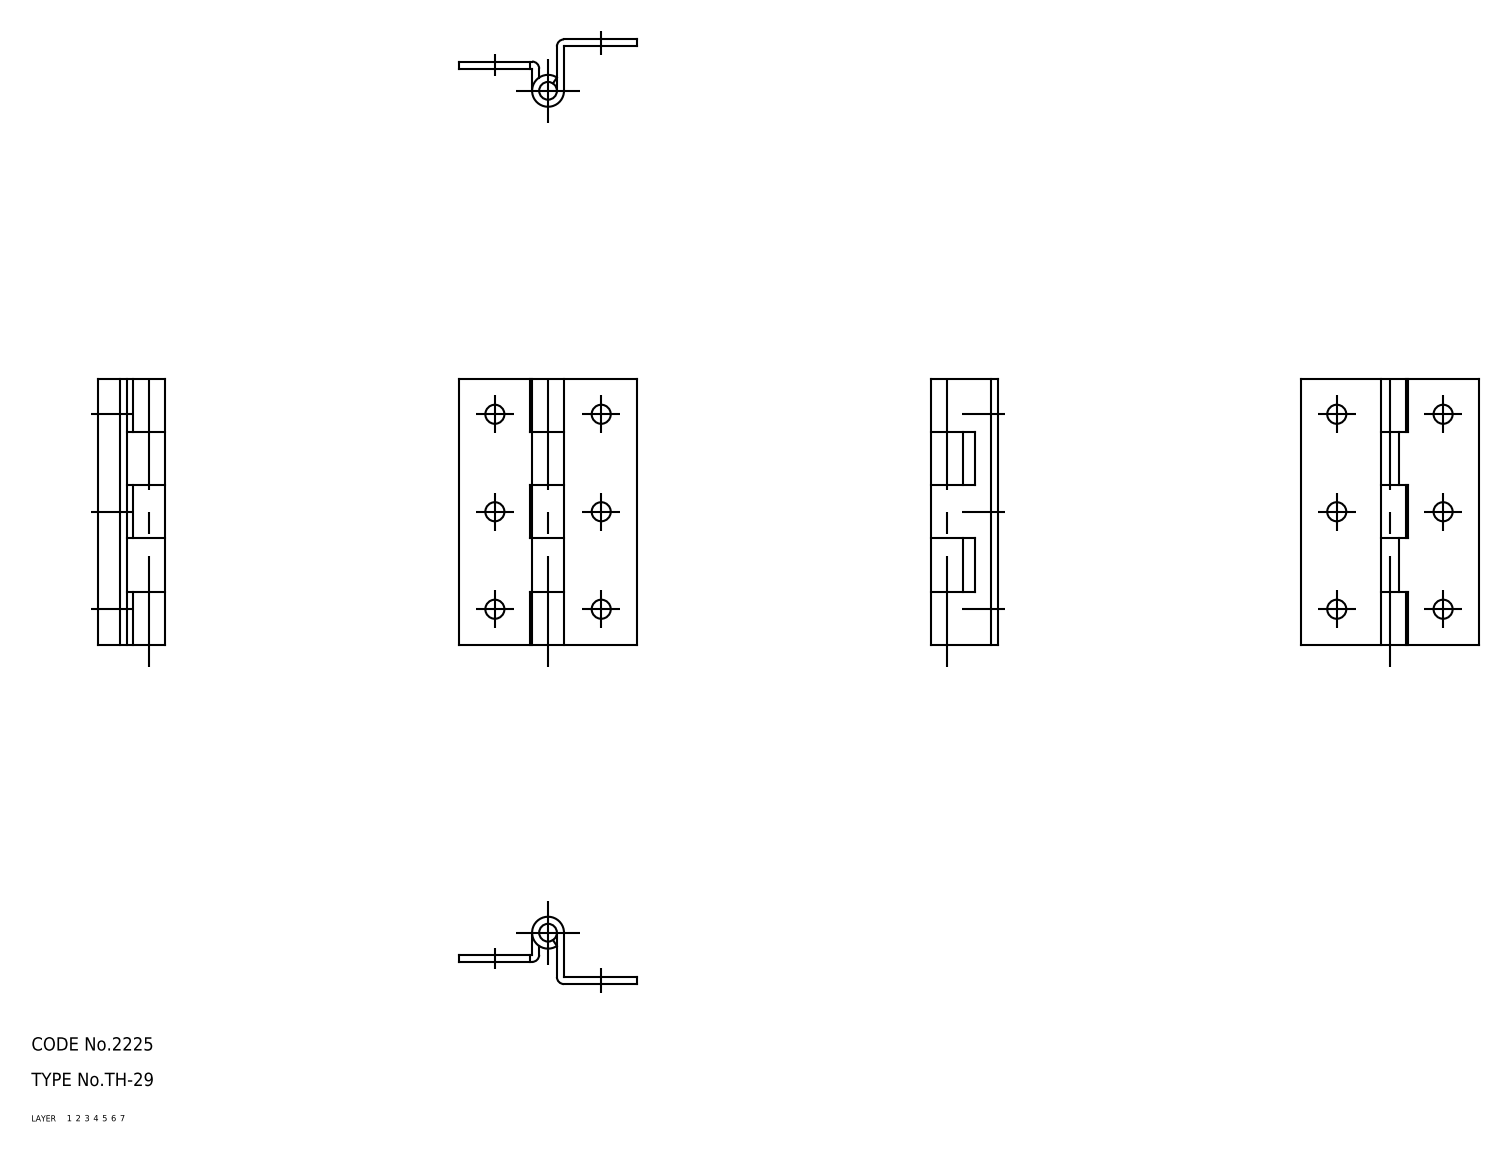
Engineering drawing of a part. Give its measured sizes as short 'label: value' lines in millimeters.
name: shaft; hinge piece_B; hinge piece_A; TH_29_7197_36
written by: CADfix (AUTOMOTIVE_DESIGN)
unit: mm
bodies: 3 solids, 63 faces (0 planar, 0 cylindrical, 63 other)
size: 60 × 40 × 15.2
volume: 6 238 mm³; area: 8 606 mm²
